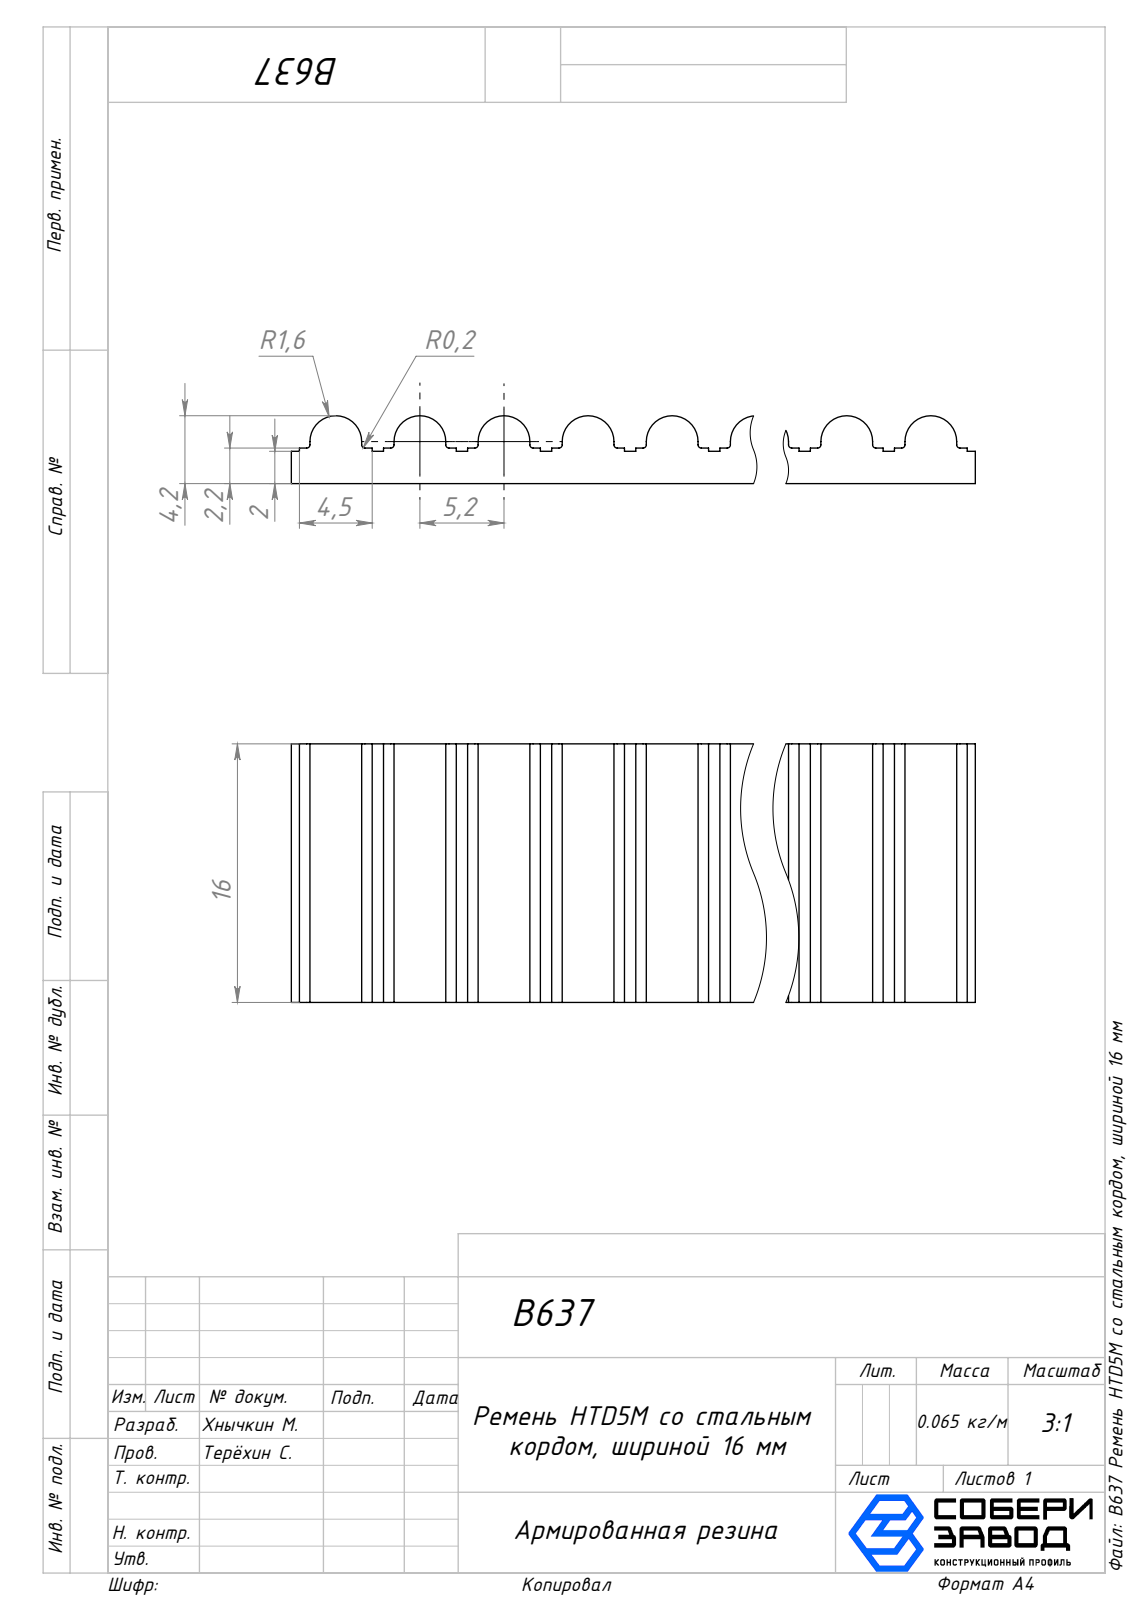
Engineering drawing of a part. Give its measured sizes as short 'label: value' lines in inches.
name: B637 Ремень HTD5M со стальным кордом, шириной 16 мм
written by: SolidWorks 2025 (AUTOMOTIVE_DESIGN)
unit: in
bodies: 1 solid, 86 faces (62 planar, 24 cylindrical, 0 other)
size: 1.65 × 0.63 × 0.165
volume: 0.13 in³; area: 3.157 in²
rounds: 16× R0.008, 8× R0.063
face distances: 0.63, 0.079, 0.087, 0.205, 0.409, 0.614, 1.65, 0.819, 0.126, 0.331
